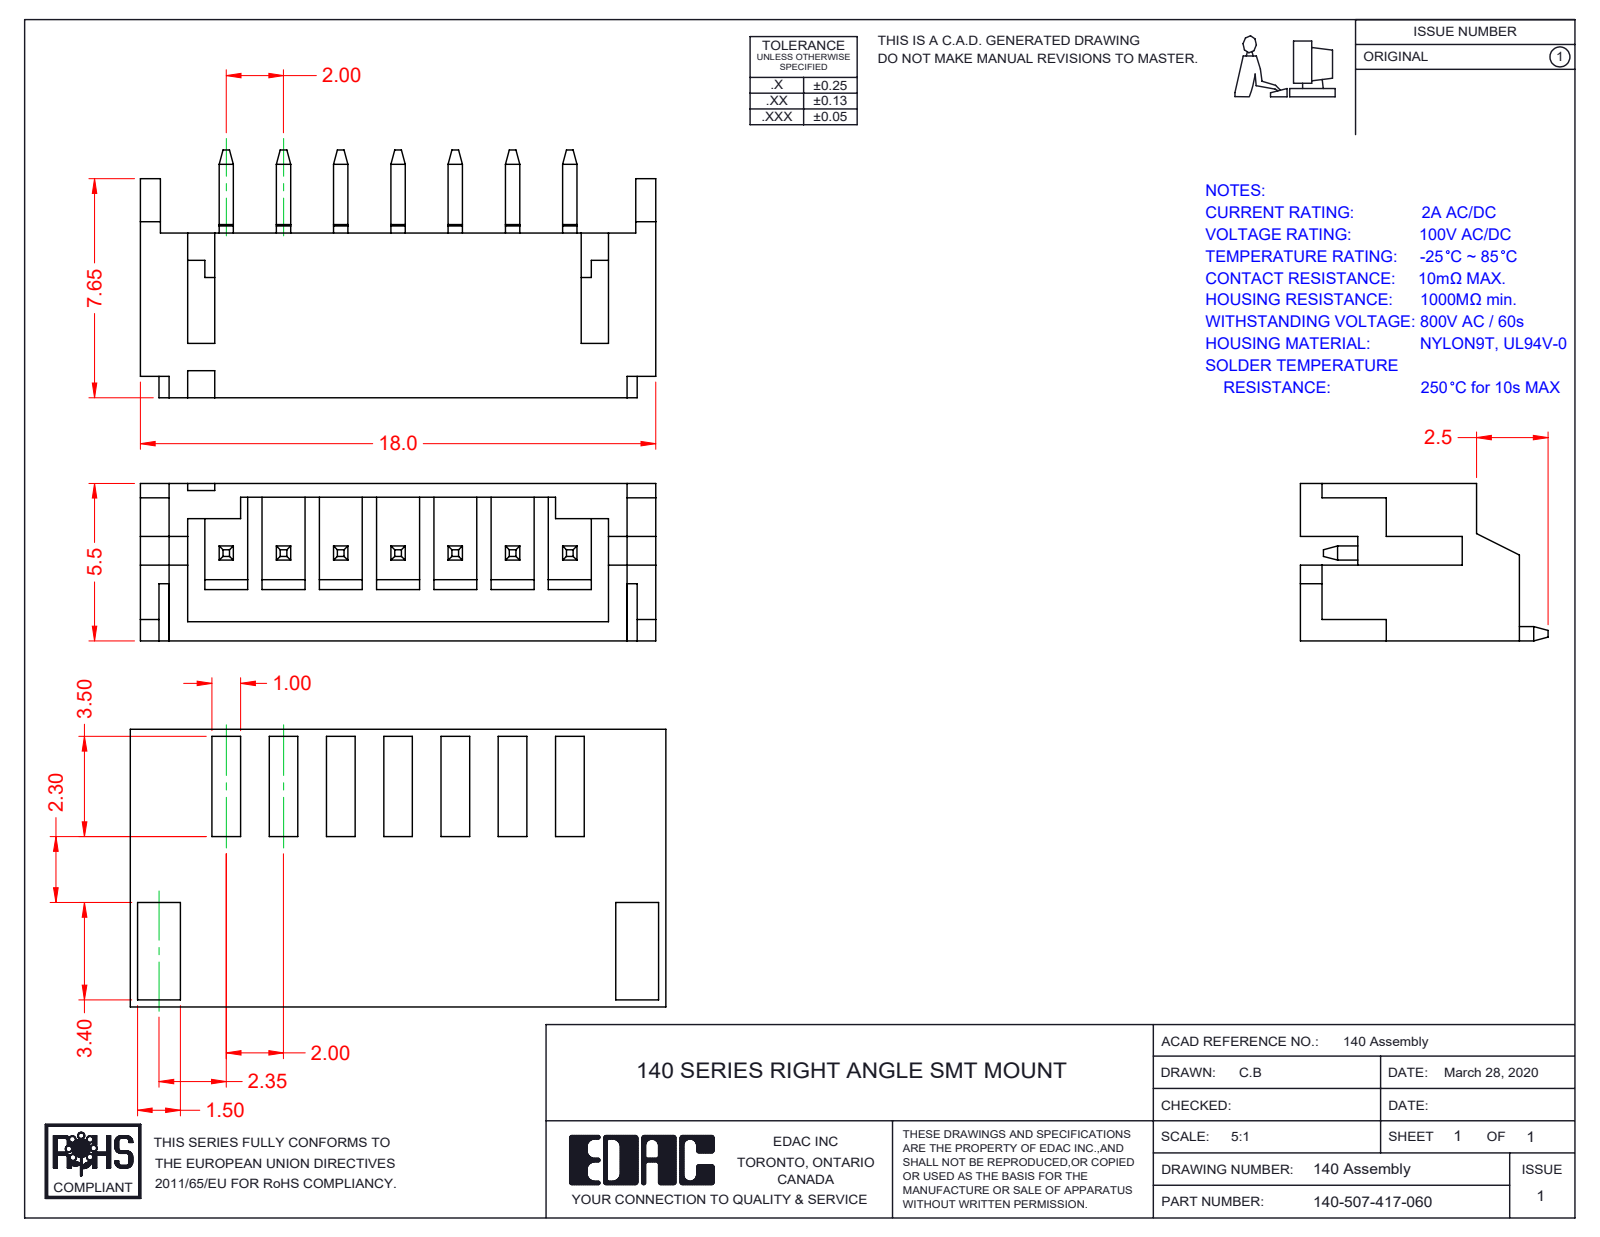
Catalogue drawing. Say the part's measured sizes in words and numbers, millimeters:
The part is named "RA SMT Pad; RA SMT Contact; 140-507-417-060; RA SMT Housing_507". Its 3-D file was written by "SolidWorks 2016 (CONFIG_CONTROL_DESIGN)". It is 10 solids with 402 faces: 374 planar, 28 cylindrical and 0 other. Overall it measures 18 by 8.65 by 5.5 millimeters. Its volume is 258 cubic millimeters and its surface area 955 square millimeters. Partial cylindrical surfaces (rounded edges, fillets, slot ends): 2 of radius 0.55. The main face-to-face distances are 0.65, 5.5, 0.67, 4.83, 0.5, 1, 16.35, 0.95, 4.35, 1.65.
